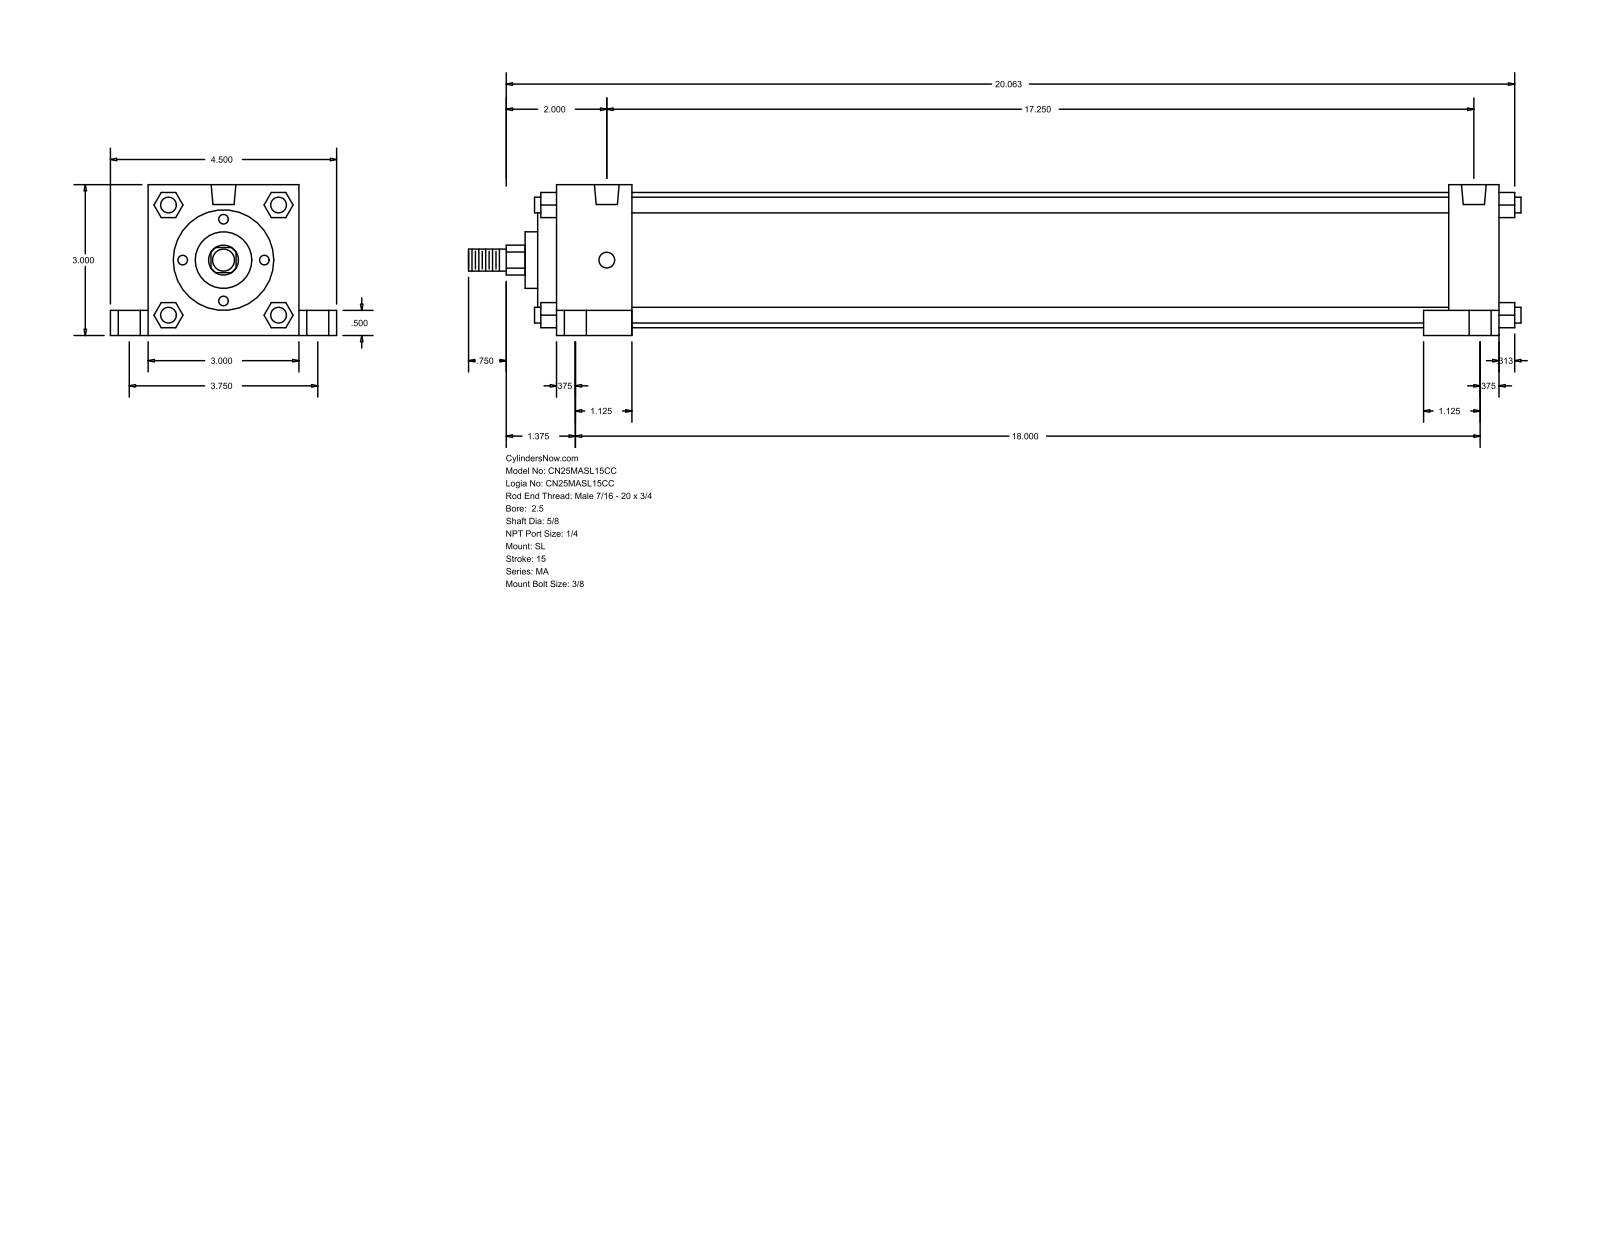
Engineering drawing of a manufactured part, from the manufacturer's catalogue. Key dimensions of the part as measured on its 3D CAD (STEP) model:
Part name (STEP PRODUCT): MA_SL__0250_0.625
STEP written by: GSSL Pune (CONFIG_CONTROL_DESIGN)
Units: millimetres
Bodies: 0 solids, 150 faces (113 planar, 37 cylindrical, 0 other)
Overall size (bounding box): 531.81 × 114.3 × 76.2
Round holes (diameter × count): ⌀7.94 ×4, ⌀11.11 ×4, ⌀17.46 ×4, ⌀12.49 ×2
Round bosses / shafts (diameter × count): ⌀7.94 ×4, ⌀68.33 ×1, ⌀50.8 ×1, ⌀28.57 ×1, ⌀15.88 ×1, ⌀11.11 ×1
Partial cylindrical surfaces — rounded edges, fillets, slot ends (radius × count): R7.54 ×1
Main face-to-face distances: 76.2, 476.25, 12.7, 412.75, 25.4, 38.1, 438.15, 450.85, 19.05, 63.5
Hole centre spacings: 47.73, 50.2, 95.24, 438.15, 443.88, 456.52, 457.2, 467.01
